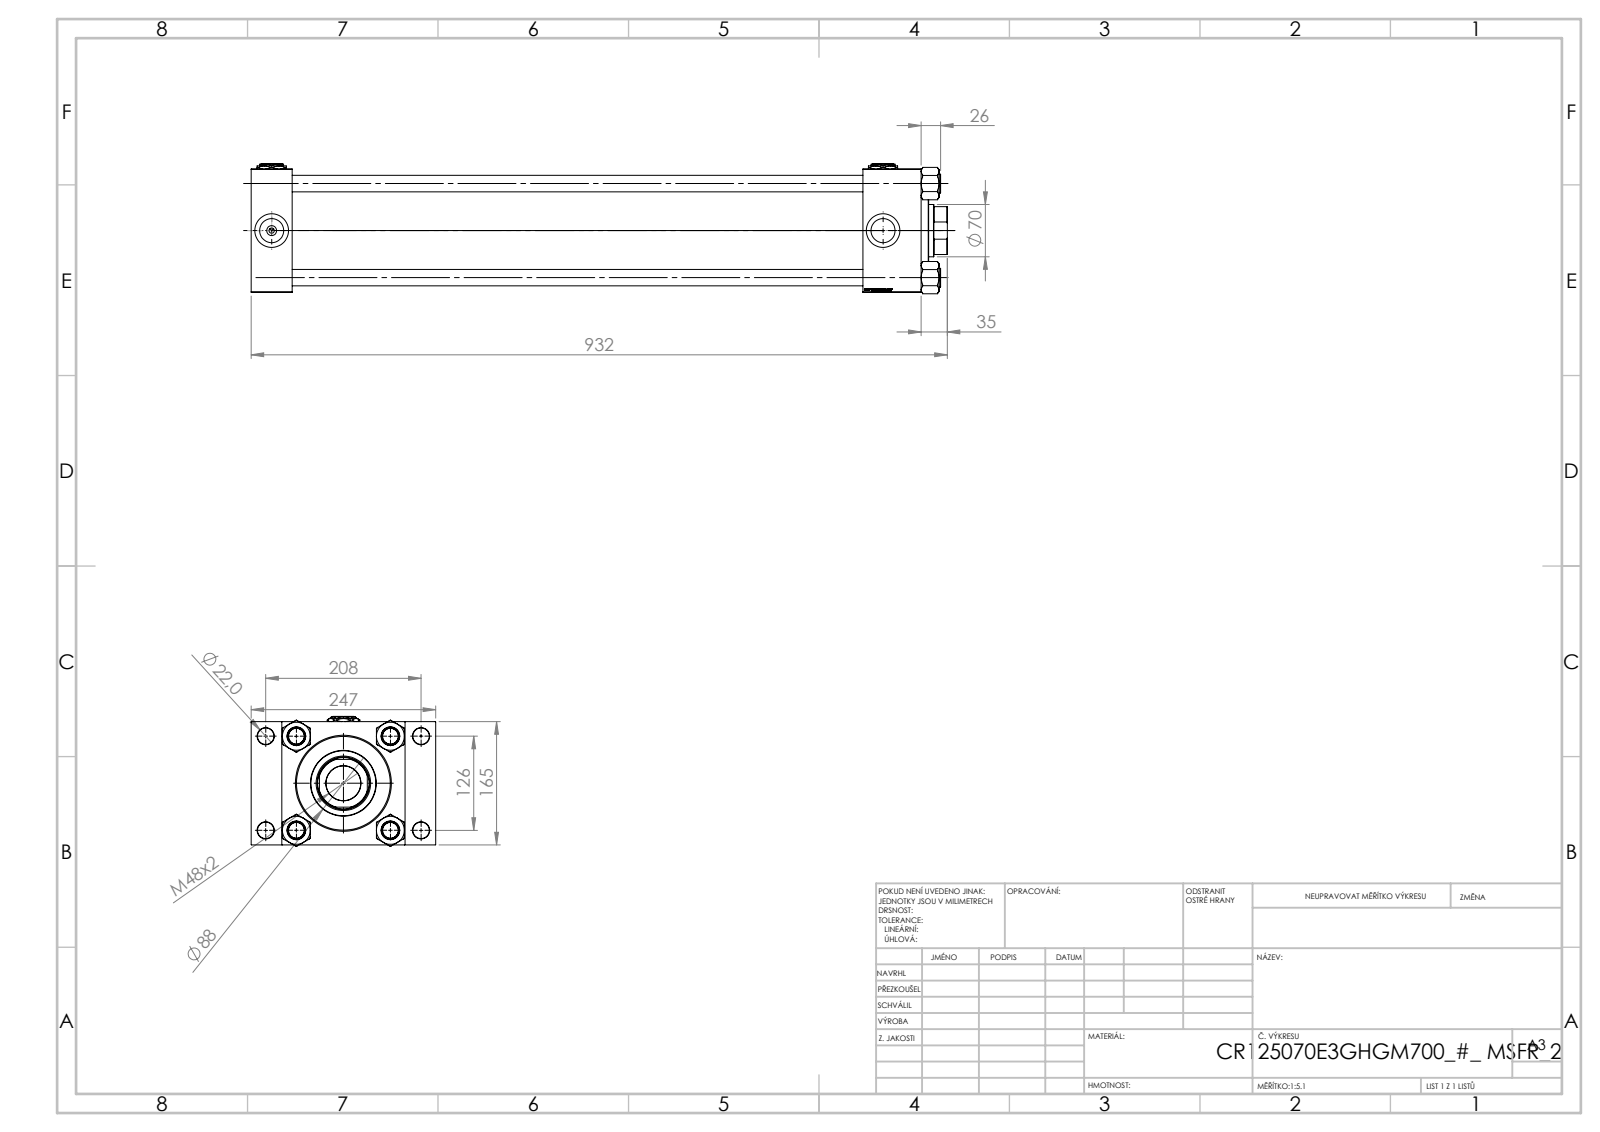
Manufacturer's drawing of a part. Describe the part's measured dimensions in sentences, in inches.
The part is named "Zatka_pro_OIL_PORT; V215_VC_A; V215CR_E_Body; V215CR_TYCINKA_E (+2 more)". Its 3-D file was written by "SolidWorks 2019 (CONFIG_CONTROL_DESIGN)". It is 13 solids with 1290 faces: 595 planar, 101 cylindrical and 594 other. Overall it measures 36.693 by 9.724 by 6.853 inches. Its volume is 593.7 cubic inches and its surface area 2 288 square inches. Round holes: 8 of diameter 0.866, 4 of diameter 1.269, 4 of diameter 1.772, 3 of diameter 0.276, 2 of diameter 0.098, 1 of diameter 1.831, 1 of diameter 2.756, 1 of diameter 2.874, 1 of diameter 3.78, 1 of diameter 4.921, 1 of diameter 4.941. Round bosses or shafts: 4 of diameter 0.984, 1 of diameter 5.157, 1 of diameter 3.465. Partial cylindrical surfaces (rounded edges, fillets, slot ends): 1 of radius 1.339. The main face-to-face distances are 2.165, 6.496, 35.315, 33.15, 1.614, 3.071, 32.244, 30.079, 8.11, 34.185. The hole center spacings are 1.616, 2.48, 3.003, 3.505, 4.787, 4.957, 5.215, 5.473.
